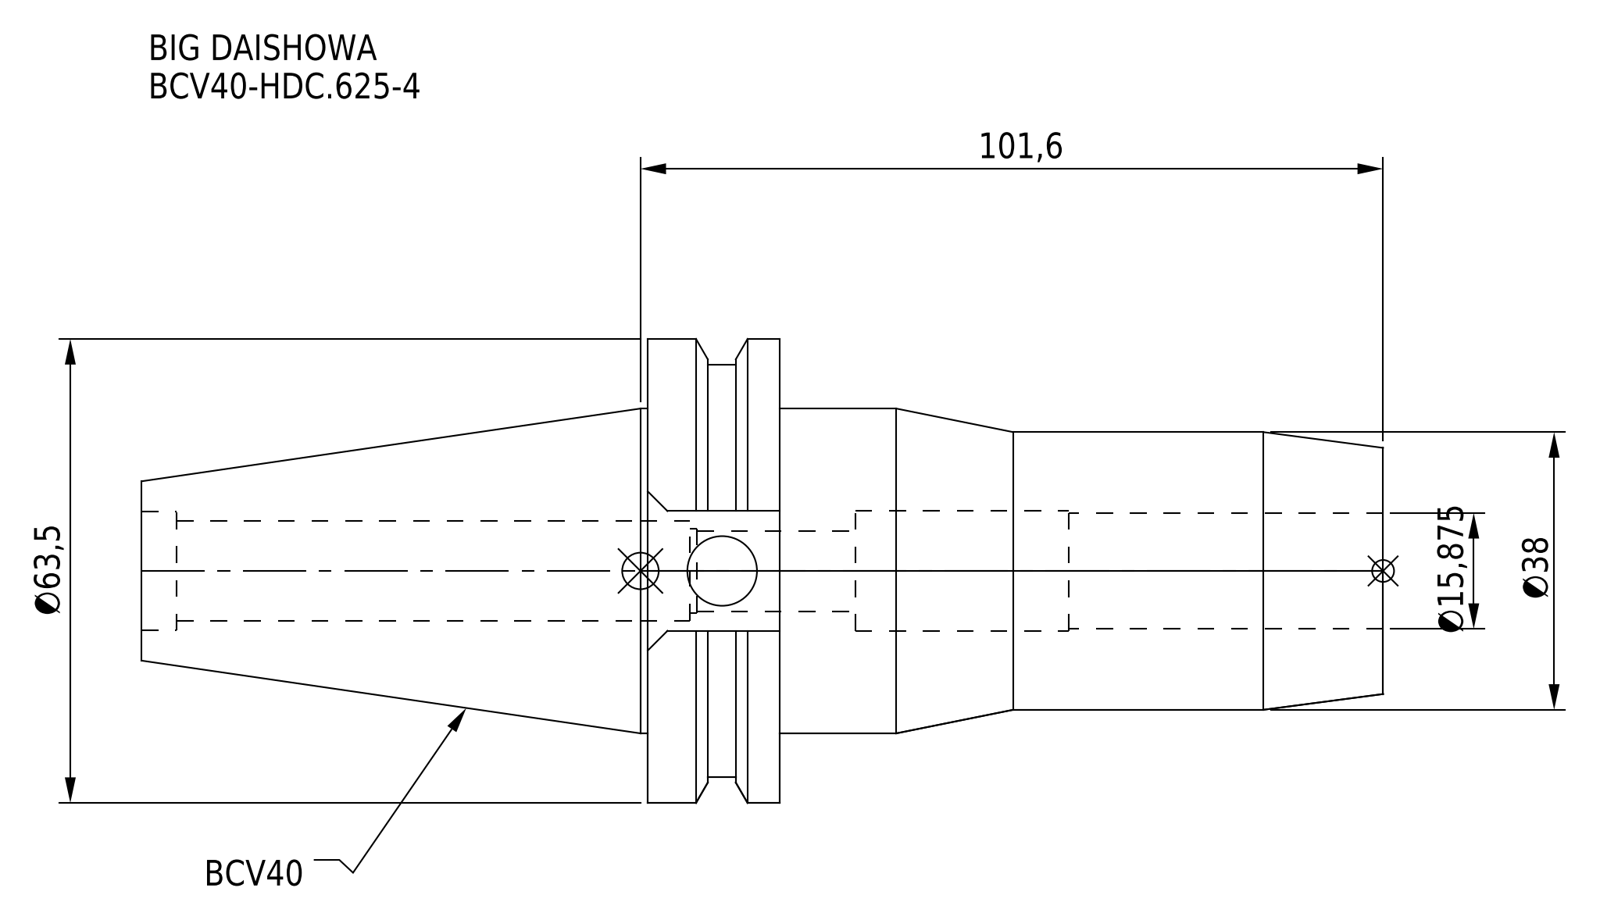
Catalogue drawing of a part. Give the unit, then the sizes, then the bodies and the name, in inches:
Units: inches
Overall size (bounding box): 6.687 × 2.5 × 2.415
Round holes (diameter × count): ⌀0.375 ×1, ⌀0.433 ×1, ⌀0.453 ×1, ⌀0.535 ×1, ⌀0.625 ×1, ⌀0.643 ×1, ⌀0.646 ×1
Round bosses / shafts (diameter × count): ⌀2.5 ×1, ⌀2.219 ×1, ⌀1.75 ×1, ⌀1.496 ×1
Main face-to-face distances: 0.711, 3.25, 3.961, 6.687, 3.437, 2.726, 1.872, 0.645, 2.843, 0.407
Volume: 11.61 in³ · Surface area: 52.88 in²
Bodies: 1 solid, 62 faces (24 planar, 28 cylindrical, 10 other)
Part name (STEP PRODUCT): BCV40-HDC_625-4
STEP written by: CREO PARAMETRIC BY PTC INC, 2016380 (AUTOMOTIVE_DESIGN)
